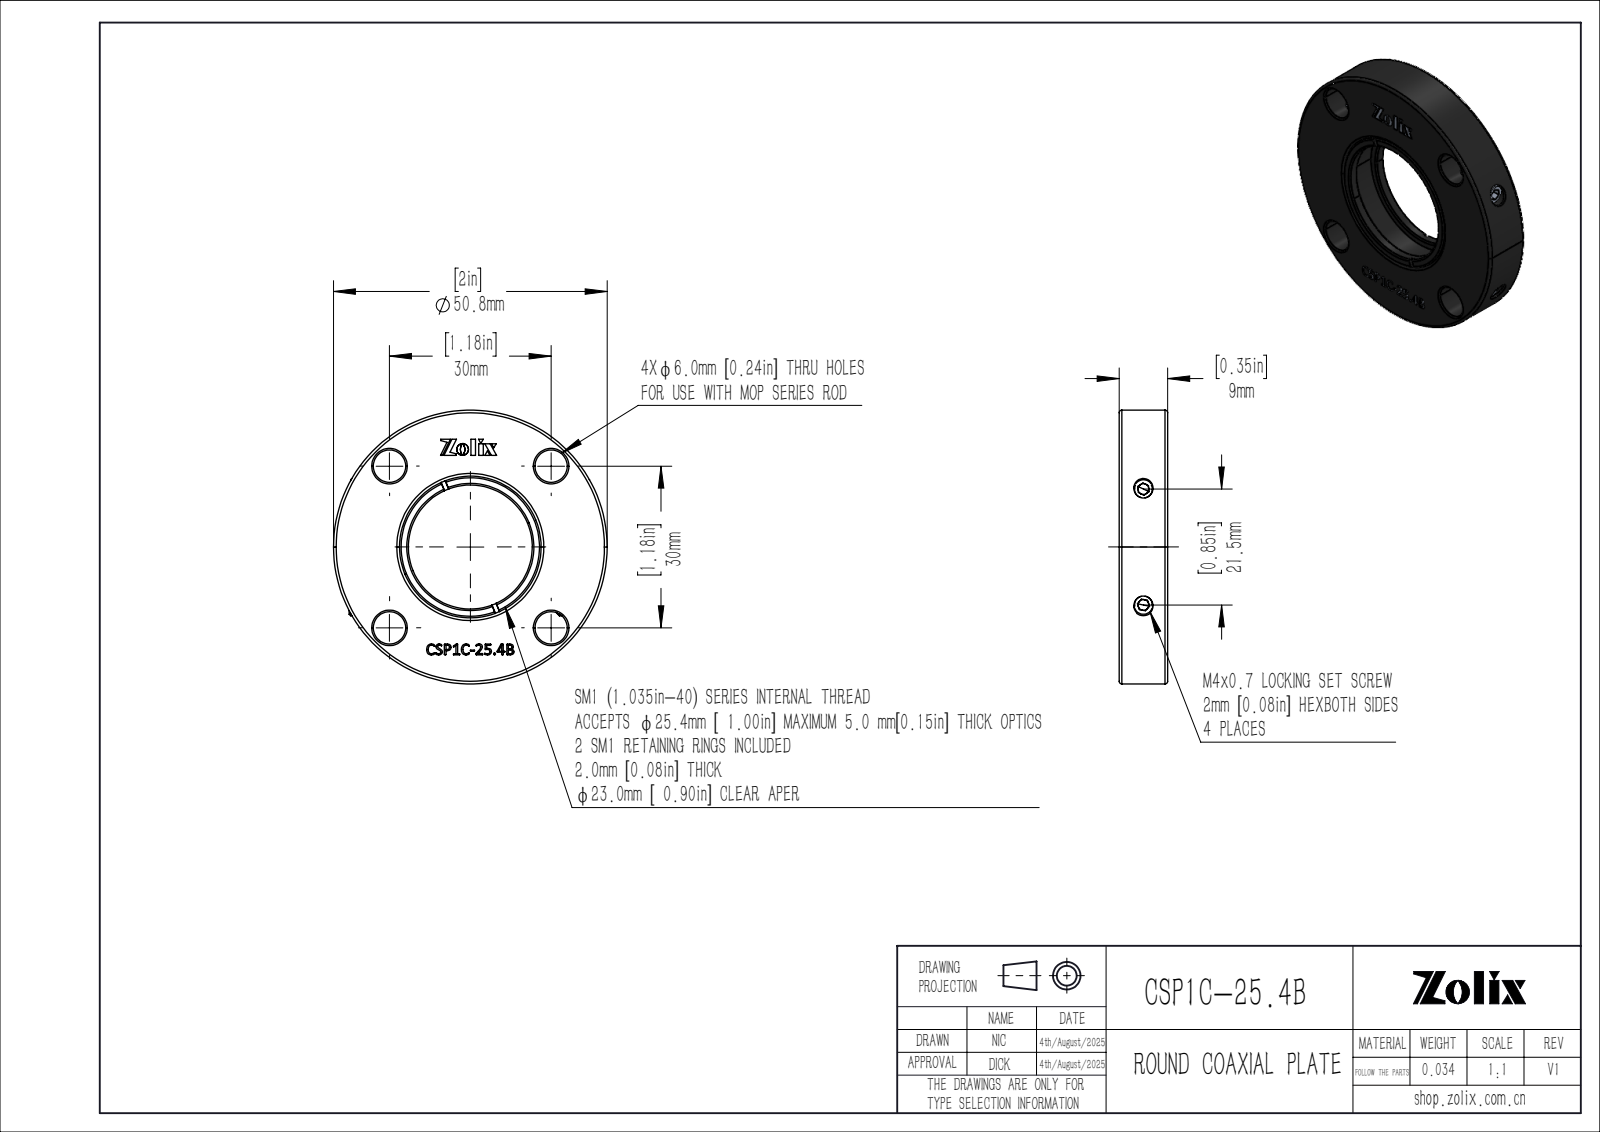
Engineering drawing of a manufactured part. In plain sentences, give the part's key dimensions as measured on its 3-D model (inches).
The part is named "CSP1C-25.4B". Its 3-D file was written by "SolidWorks 2020 (CONFIG_CONTROL_DESIGN)". It is 7 solids with 537 faces: 304 planar, 44 cylindrical and 189 other. Overall it measures 2 by 2 by 0.354 inches. Its volume is 0.773 cubic inches and its surface area 11.31 square inches. Round holes: 4 of diameter 0.236, 2 of diameter 0.13, 1 of diameter 0.906. Round bosses or shafts: 2 of diameter 0.157, 1 of diameter 2, 1 of diameter 1.035. The main face-to-face distances are 0.354, 0.081, 0.274, 0.193, 0.354, 0.273, 0.08, 0.078, 0.079, 0.024. The hole center spacings are 0.835, 1.181, 1.67, 0.846.
